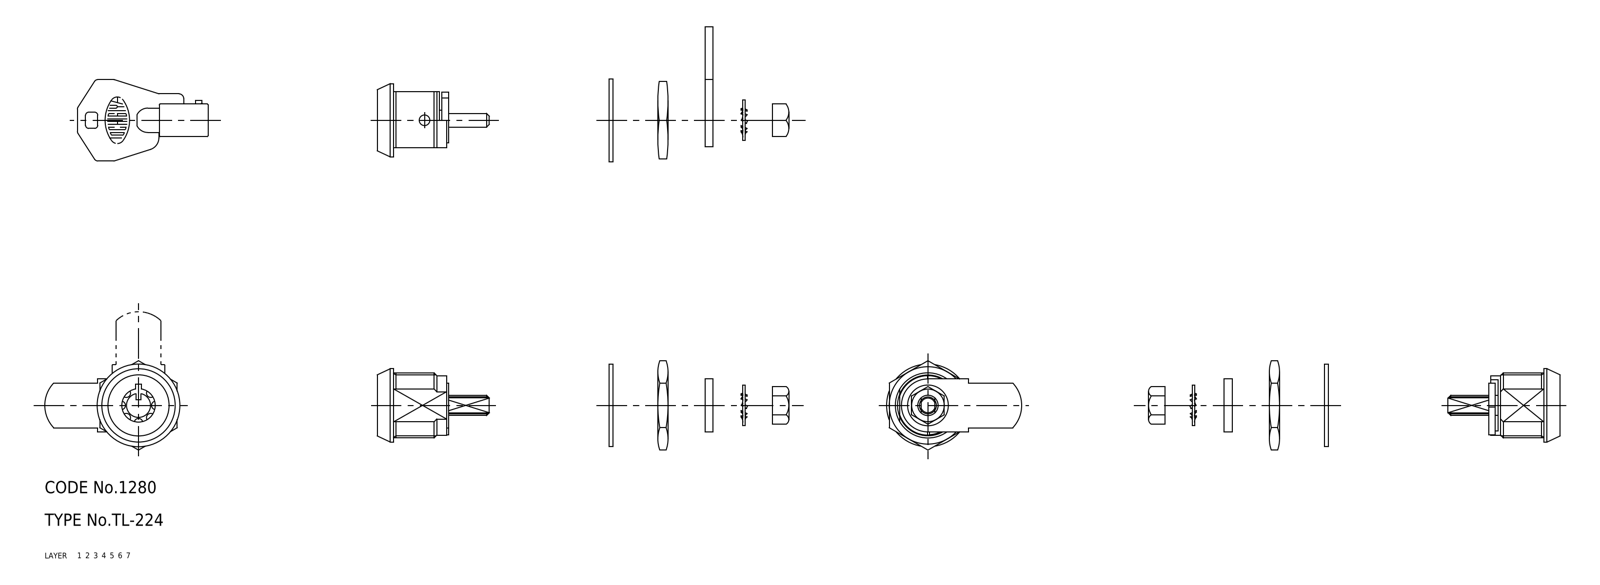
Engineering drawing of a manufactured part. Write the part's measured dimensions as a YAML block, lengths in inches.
part_name: "washer_2; washer_1; nut_B; nut_A (+5 more)"
step_written_by: "CADfix (AUTOMOTIVE_DESIGN)"
units: inches
bodies: {solids: 8, faces: 162, planar: 0, cylindrical: 0, other: 162}
overall_size: [4.104, 1.305, 0.864]
volume: 0.32
surface_area: 8.378
